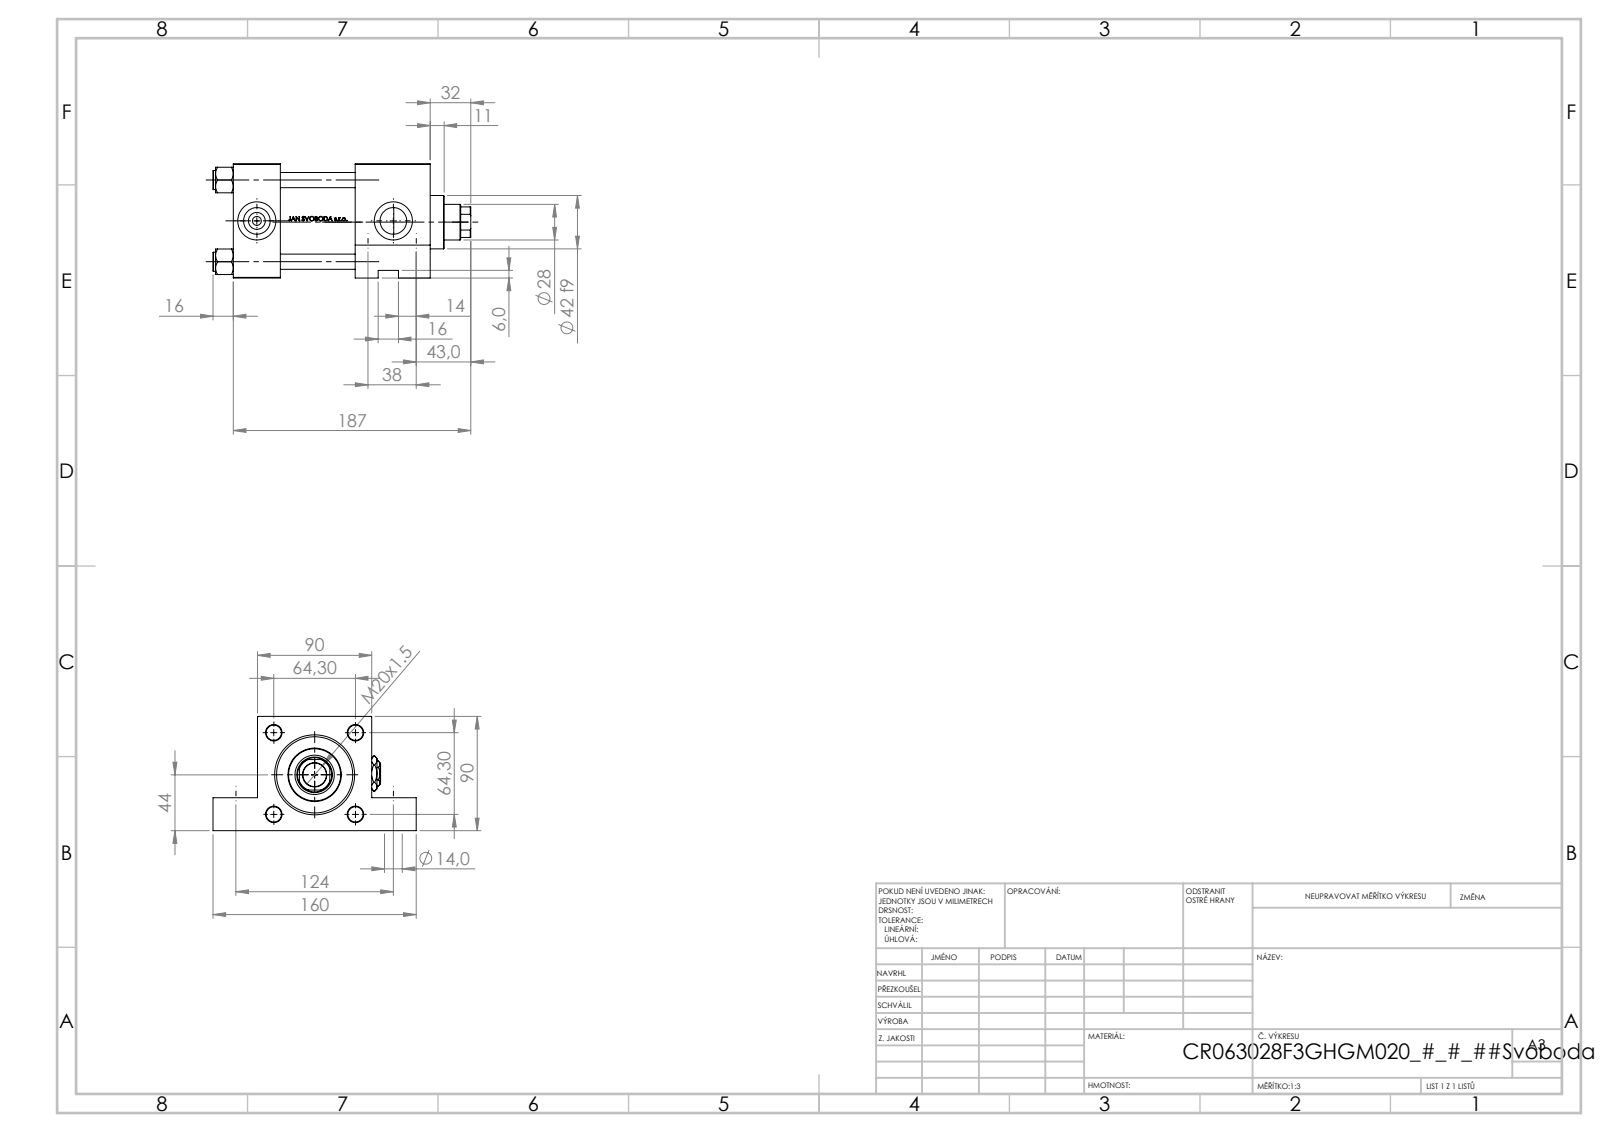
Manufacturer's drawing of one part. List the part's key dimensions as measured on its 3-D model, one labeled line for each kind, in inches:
Part name (STEP PRODUCT): V215_VC_A; V215CR_VCP_F; Zatka_pro_OIL_PORT; V215CR_F_Body (+2 more)
STEP written by: SolidWorks 2019 (CONFIG_CONTROL_DESIGN)
Units: inches
Bodies: 13 solids, 1200 faces (484 planar, 134 cylindrical, 582 other)
Overall size (bounding box): 7.992 × 6.299 × 3.543
Volume: 62.43 in³ · Surface area: 307.9 in²
Round holes (diameter × count): ⌀0.472 ×4, ⌀0.825 ×3, ⌀1.181 ×3, ⌀0.276 ×2, ⌀0.551 ×2, ⌀0.551 ×2, ⌀0.728 ×1, ⌀0.787 ×1, ⌀1.102 ×1, ⌀1.22 ×1, ⌀1.969 ×1, ⌀2.362 ×1
Round bosses / shafts (diameter × count): ⌀0.591 ×4, ⌀2.717 ×1, ⌀1.654 ×1
Partial cylindrical surfaces — rounded edges, fillets, slot ends (radius × count): R0.531 ×1
Main face-to-face distances: 3.543, 2.323, 1.457, 4.646, 6.102, 3.78, 0.787, 1.024, 2.52, 4.921
Hole centre spacings: 2.531, 1.496, 1.763, 1.818, 3.58, 4.882, 5.106, 0.394
